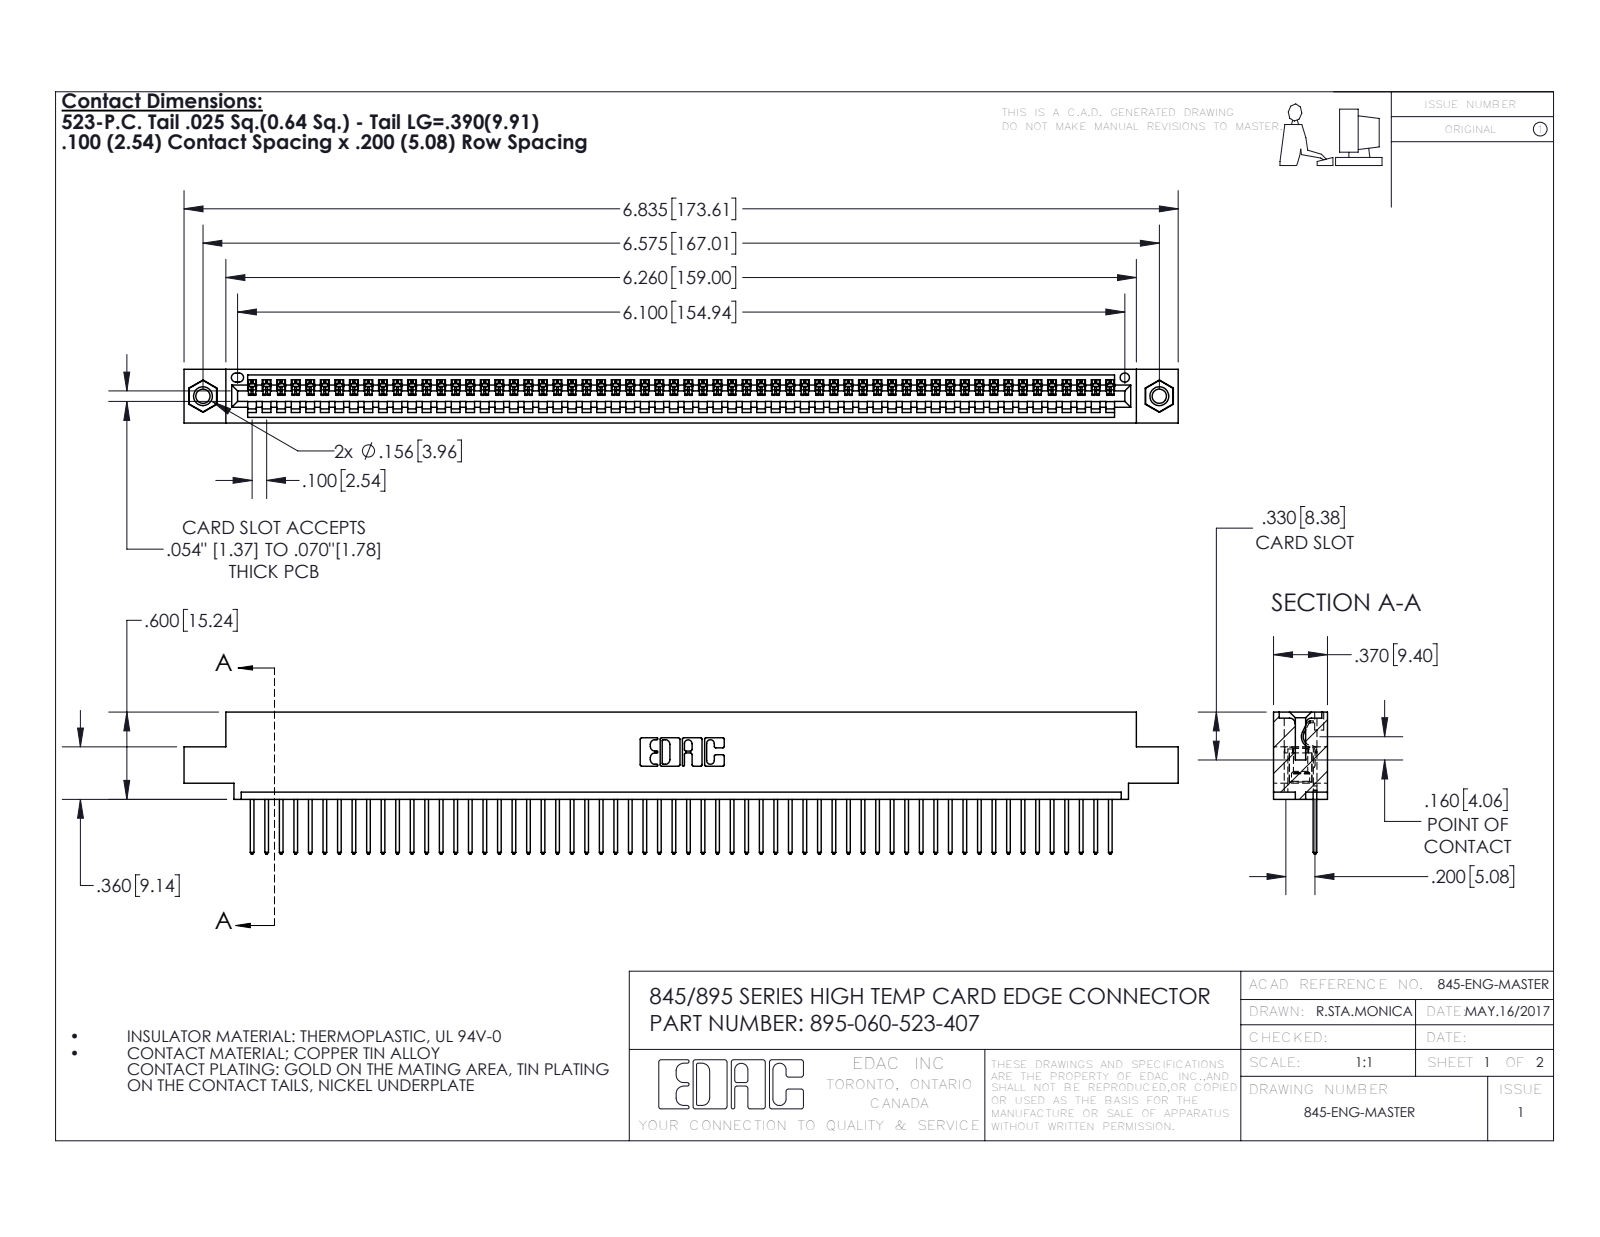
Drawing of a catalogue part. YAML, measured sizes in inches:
part_name: "345-292-001_345-293-123; 395-060-523-407; 345 Part_0.110 Offset - 0.156 Dia-TI; 345-250-001_345-250-005-103"
step_written_by: "SolidWorks 2016 (CONFIG_CONTROL_DESIGN)"
units: inches
bodies: {solids: 63, faces: 3670, planar: 2516, cylindrical: 1138, other: 16}
overall_size: [6.835, 0.977, 0.37]
volume: 1.009
surface_area: 34.7
round_holes:
  - {diameter: 0.098, count: 2}
  - {diameter: 0.125, count: 2}
  - {diameter: 0.156, count: 2}
  - {diameter: 0.064, count: 1}
round_bosses_or_shafts:
  - {diameter: 0.155, count: 2}
partial_cylinders:
  - {radius: 0.006, count: 120}
  - {radius: 0.01, count: 120}
  - {radius: 0.01, count: 22}
  - {radius: 0.007, count: 6}
  - {radius: 0.031, count: 6}
  - {radius: 0.026, count: 3}
  - {radius: 0.031, count: 2}
  - {radius: 0.04, count: 2}
face_to_face_distances: [0.072, 0.298, 0.37, 0.098, 0.272, 0.025, 0.2, 0.225, 0.149, 0.072]
hole_center_spacings: [0.27, 6.339, 6.575]
